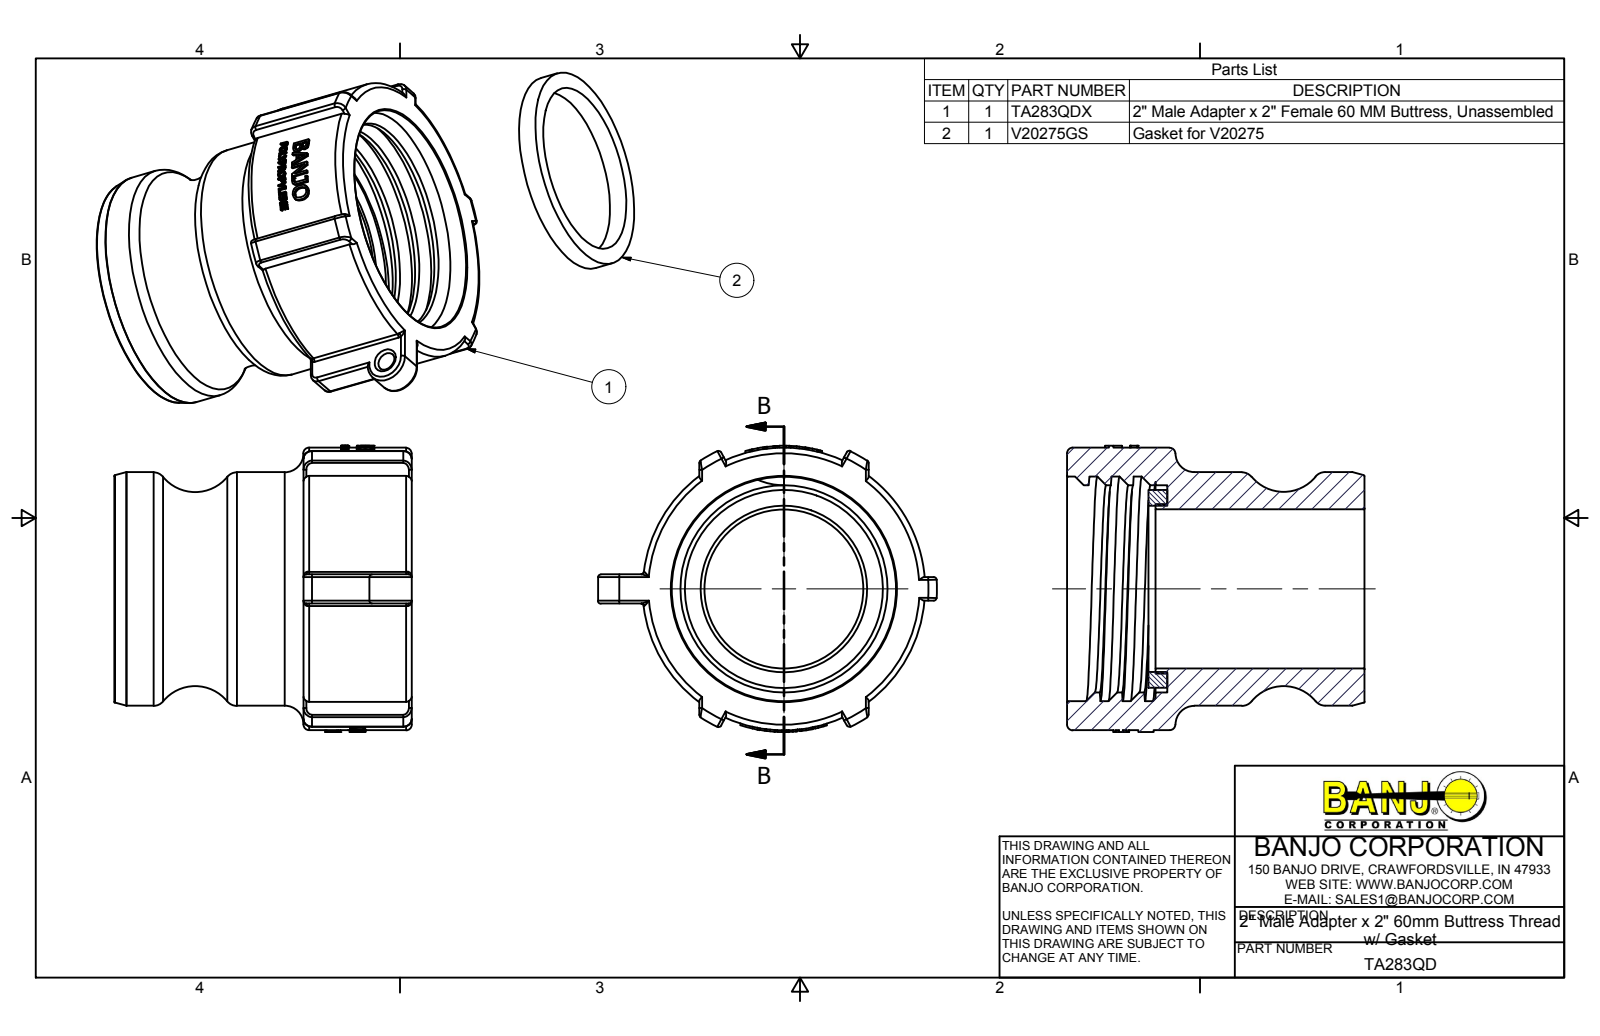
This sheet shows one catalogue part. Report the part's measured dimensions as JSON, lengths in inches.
{"part_name": "TA283QD; TA283QDX; V20275GS", "step_written_by": "Autodesk Inventor 2022 (AUTOMOTIVE_DESIGN)", "units": "inches", "bodies": {"solids": 2, "faces": 562, "planar": 216, "cylindrical": 108, "other": 238}, "overall_size": [3.6, 3.16, 3.04], "volume_in3": 8.463, "surface_area_in2": 64.88, "round_holes": [[0.2, 1], [1.688, 1], [1.765, 1], [2.2, 1], [2.385, 1]], "round_bosses_or_shafts": [[3, 1], [2.48, 1], [2.1, 1], [1.8, 1]], "partial_cylinders_radius": [[0.03, 34], [0.09, 1], [0.225, 1], [0.689, 1], [1.52, 1], [1.625, 1]], "face_to_face_distances": [2.095, 3.16, 1.065, 2.295, 0.2, 0.865, 2.22, 0.125, 0.075, 0.94]}
